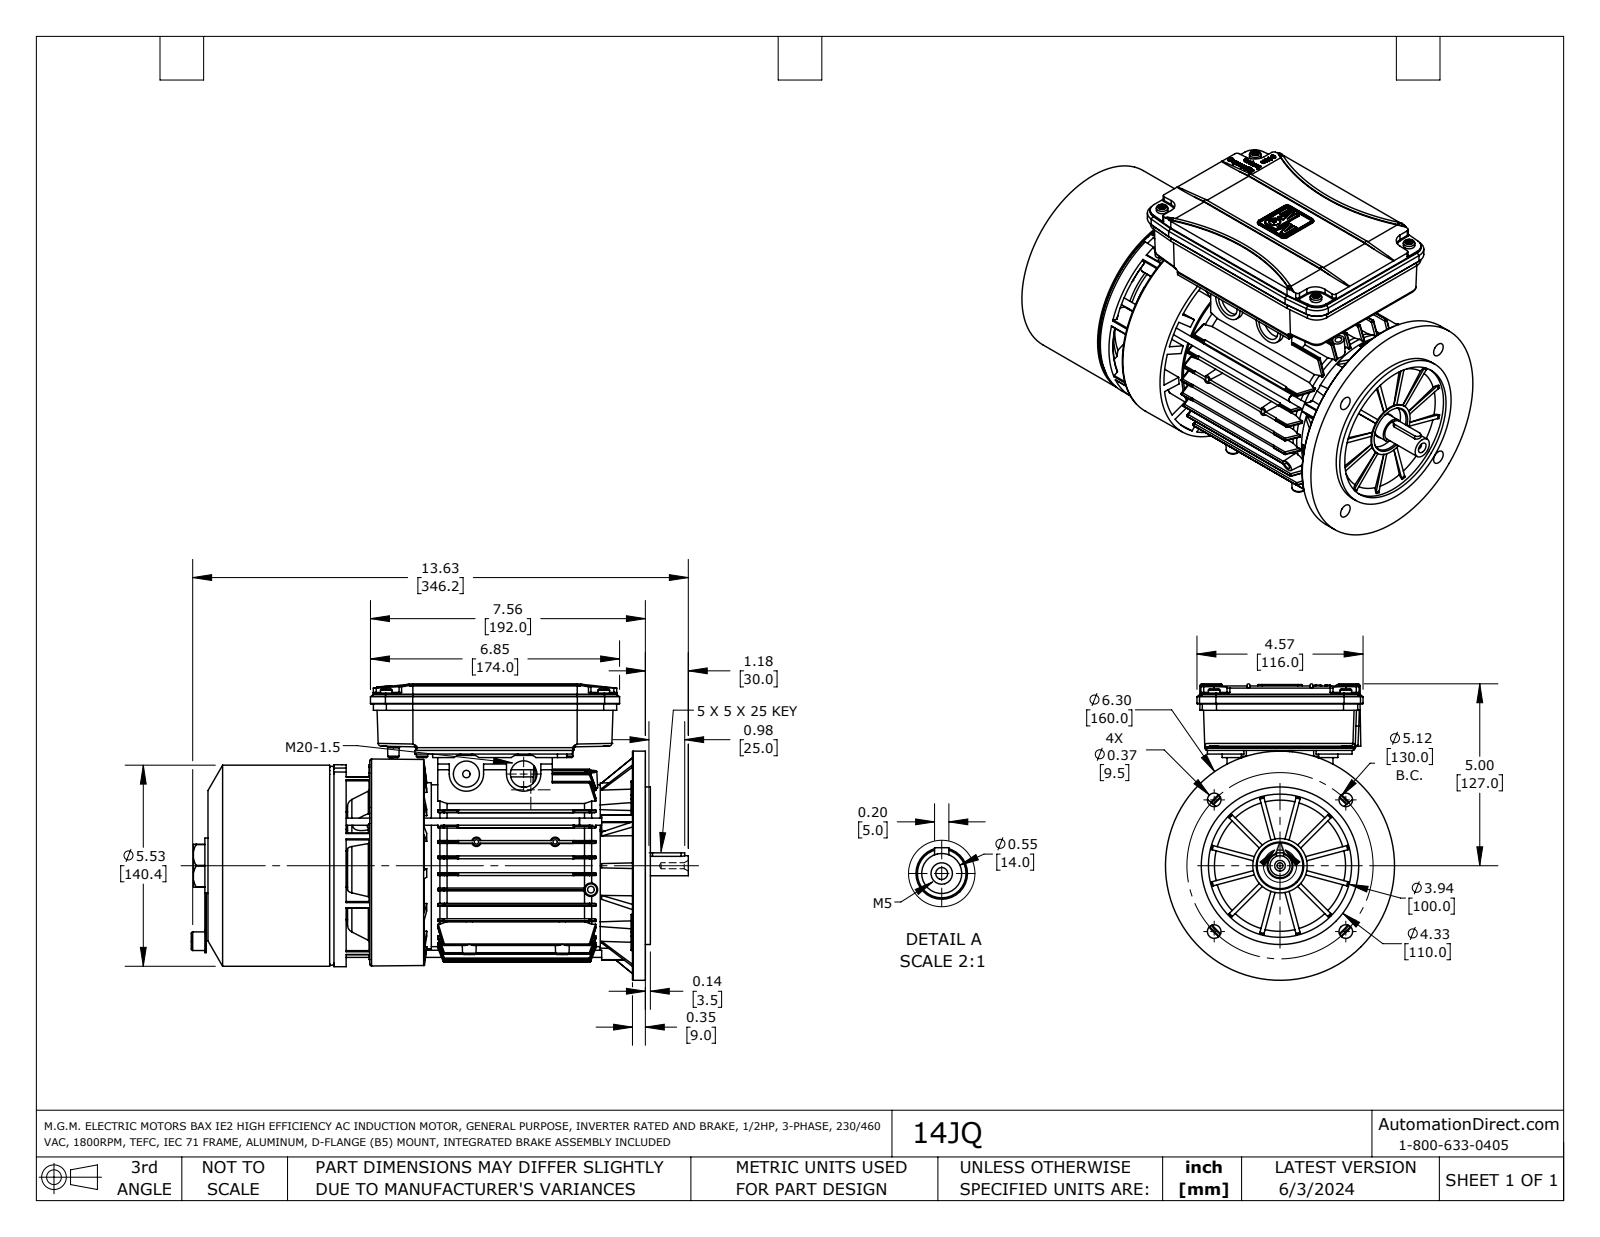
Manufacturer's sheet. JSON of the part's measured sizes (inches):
{"part_name": "14JQ", "step_written_by": "SolidWorks 2021 (AUTOMOTIVE_DESIGN)", "units": "inches", "bodies": {"solids": 22, "faces": 3823, "planar": 1380, "cylindrical": 1038, "other": 1405}, "overall_size": [13.668, 8.15, 6.299], "volume_in3": 70.4, "surface_area_in2": 1108, "round_holes": [[0.13, 21], [0.177, 12], [0.236, 11], [0.157, 8], [0.098, 7], [0.217, 7], [0.118, 6], [0.165, 4], [0.374, 4], [0.276, 3], [0.185, 2], [0.228, 1]], "round_bosses_or_shafts": [[0.177, 8], [0.118, 8], [0.315, 4], [0.197, 3], [6.299, 1], [5.551, 1], [5.528, 1], [5.425, 1]], "partial_cylinders_radius": [[0.02, 62], [0.035, 60], [0.039, 48], [0.008, 32], [0.079, 31], [0.012, 24], [0.004, 16], [0.024, 16]], "face_to_face_distances": [0.079, 0.422, 0.843, 1.726, 1.305, 2.57, 0.343, 2.148, 0.5, 1.265], "hole_center_spacings": [0.472, 2.84, 2.559, 0.818, 2.018, 2.026, 2.467, 4.187]}
